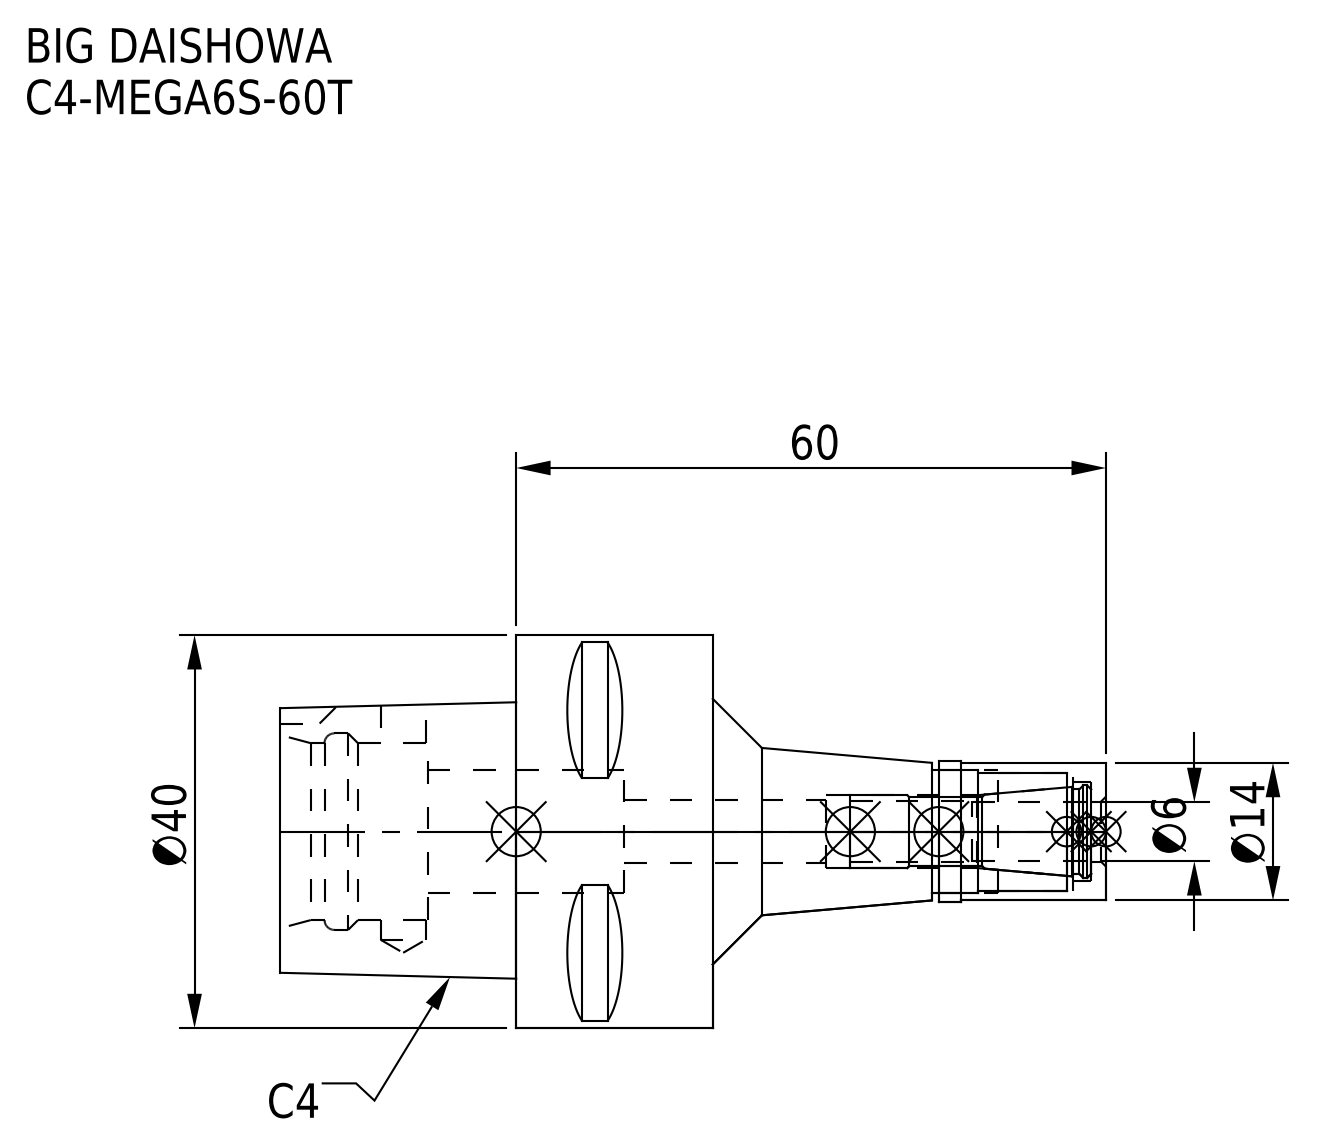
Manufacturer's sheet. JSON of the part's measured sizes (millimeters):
{"part_name": "MGN6S_1.stp; C4-MEGA6S-60T-060.stp; C4-MEGA6S-60T-060_ASM.stp; C4-MEGA6S-60T_1.stp (+3 more)", "step_written_by": "SolidWorks 2019 (CONFIG_CONTROL_DESIGN)", "units": "millimeters", "bodies": {"solids": 2, "faces": 90, "planar": 37, "cylindrical": 35, "other": 18}, "overall_size": [84, 40, 40], "volume_mm3": 37954, "surface_area_mm2": 12881, "round_holes": [[4.6, 1], [6.1, 1], [6.4, 1], [7.4, 1], [10, 1], [12, 1], [12.5, 1], [18, 1], [20, 1]], "round_bosses_or_shafts": [[40, 1], [14.3, 1], [14, 1]], "partial_cylinders_radius": [[3, 1]], "face_to_face_distances": [20, 9, 44, 24, 29, 15, 15.52, 40, 69, 60]}
